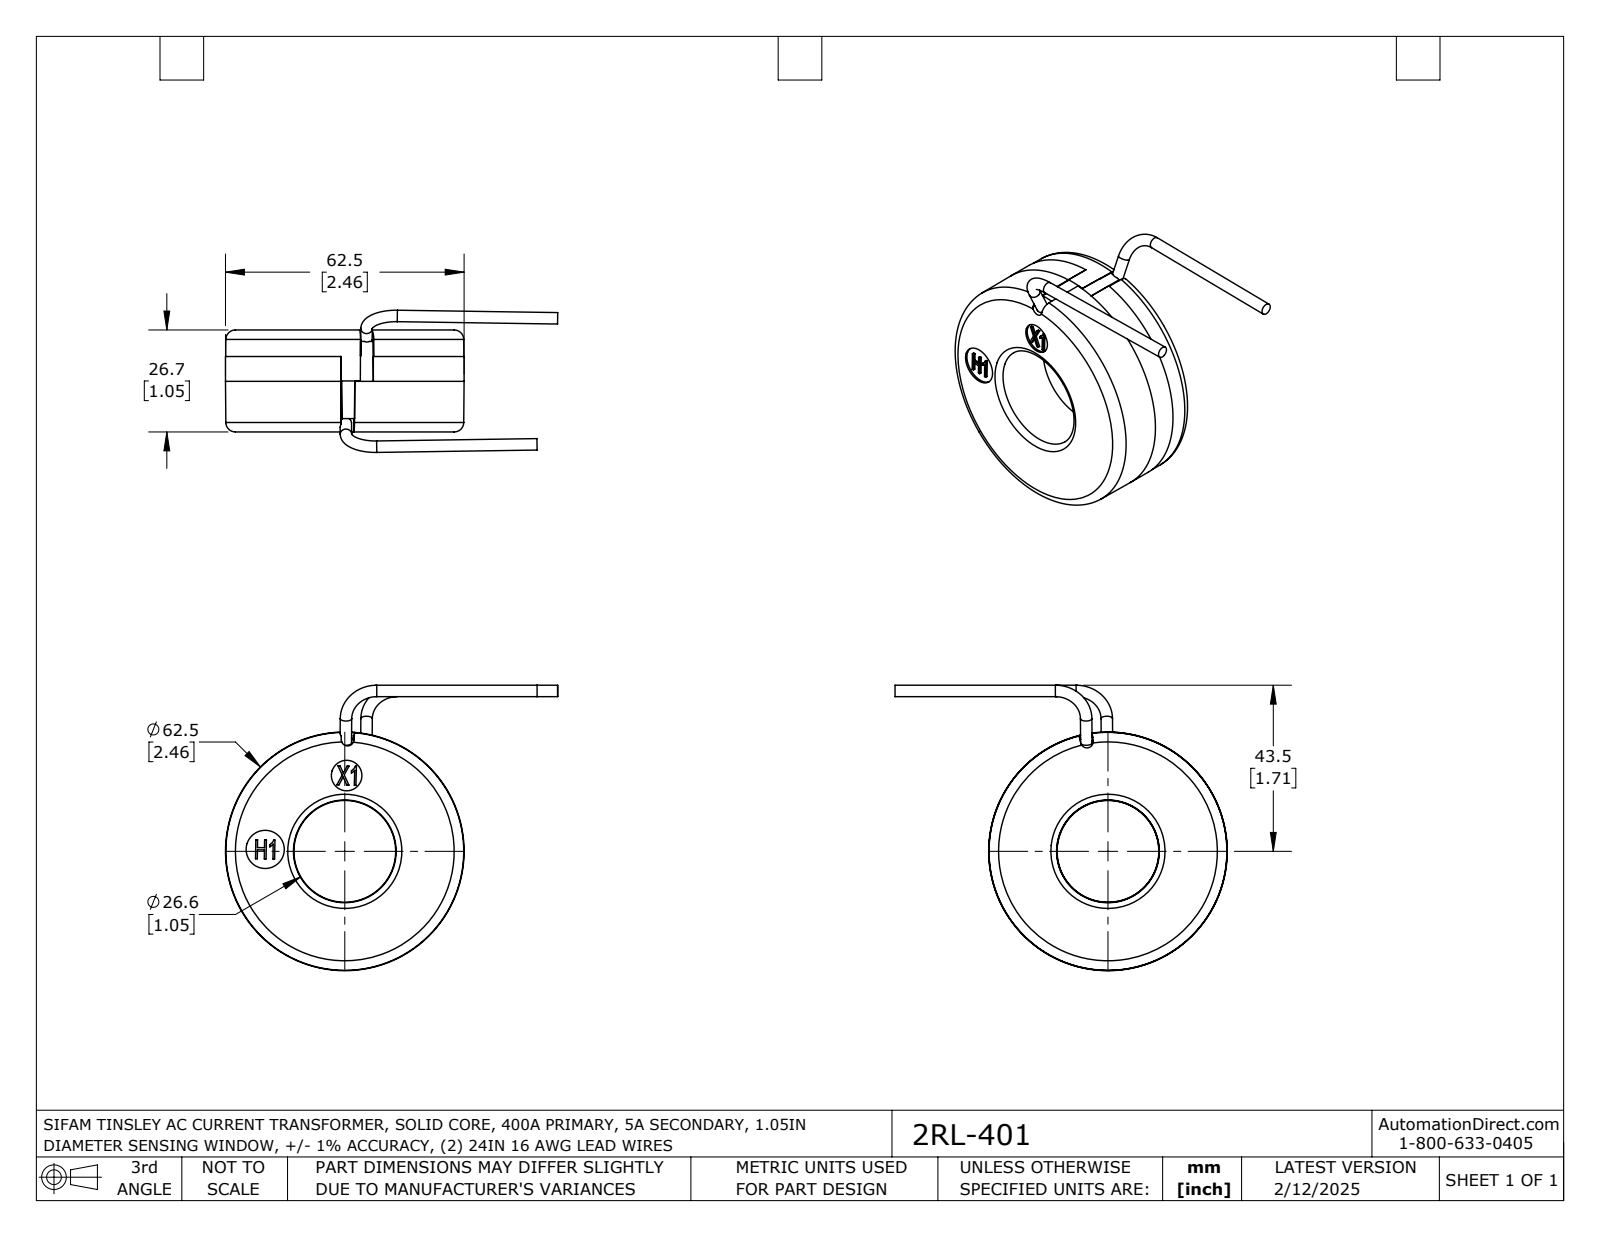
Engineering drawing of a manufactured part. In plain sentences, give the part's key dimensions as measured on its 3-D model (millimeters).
The part is named "2RL-401". Its 3-D file was written by "SolidWorks 2021 (AUTOMOTIVE_DESIGN)". It is 1 solid with 129 faces: 62 planar, 18 cylindrical and 49 other. Overall it measures 87.4 by 74.8 by 37.2 millimeters. Its volume is 66 680 cubic millimeters and its surface area 13 430 square millimeters. Round holes: 1 of diameter 8, 1 of diameter 10, 1 of diameter 60.5. Round bosses or shafts: 4 of diameter 3, 1 of diameter 62.5. The main face-to-face distances are 26.7, 0.5, 26.2, 0.5, 26.2, 19.8, 19.3, 19.3, 7, 13.4. The hole center spacings are 19.9, 20.9, 28.8.
